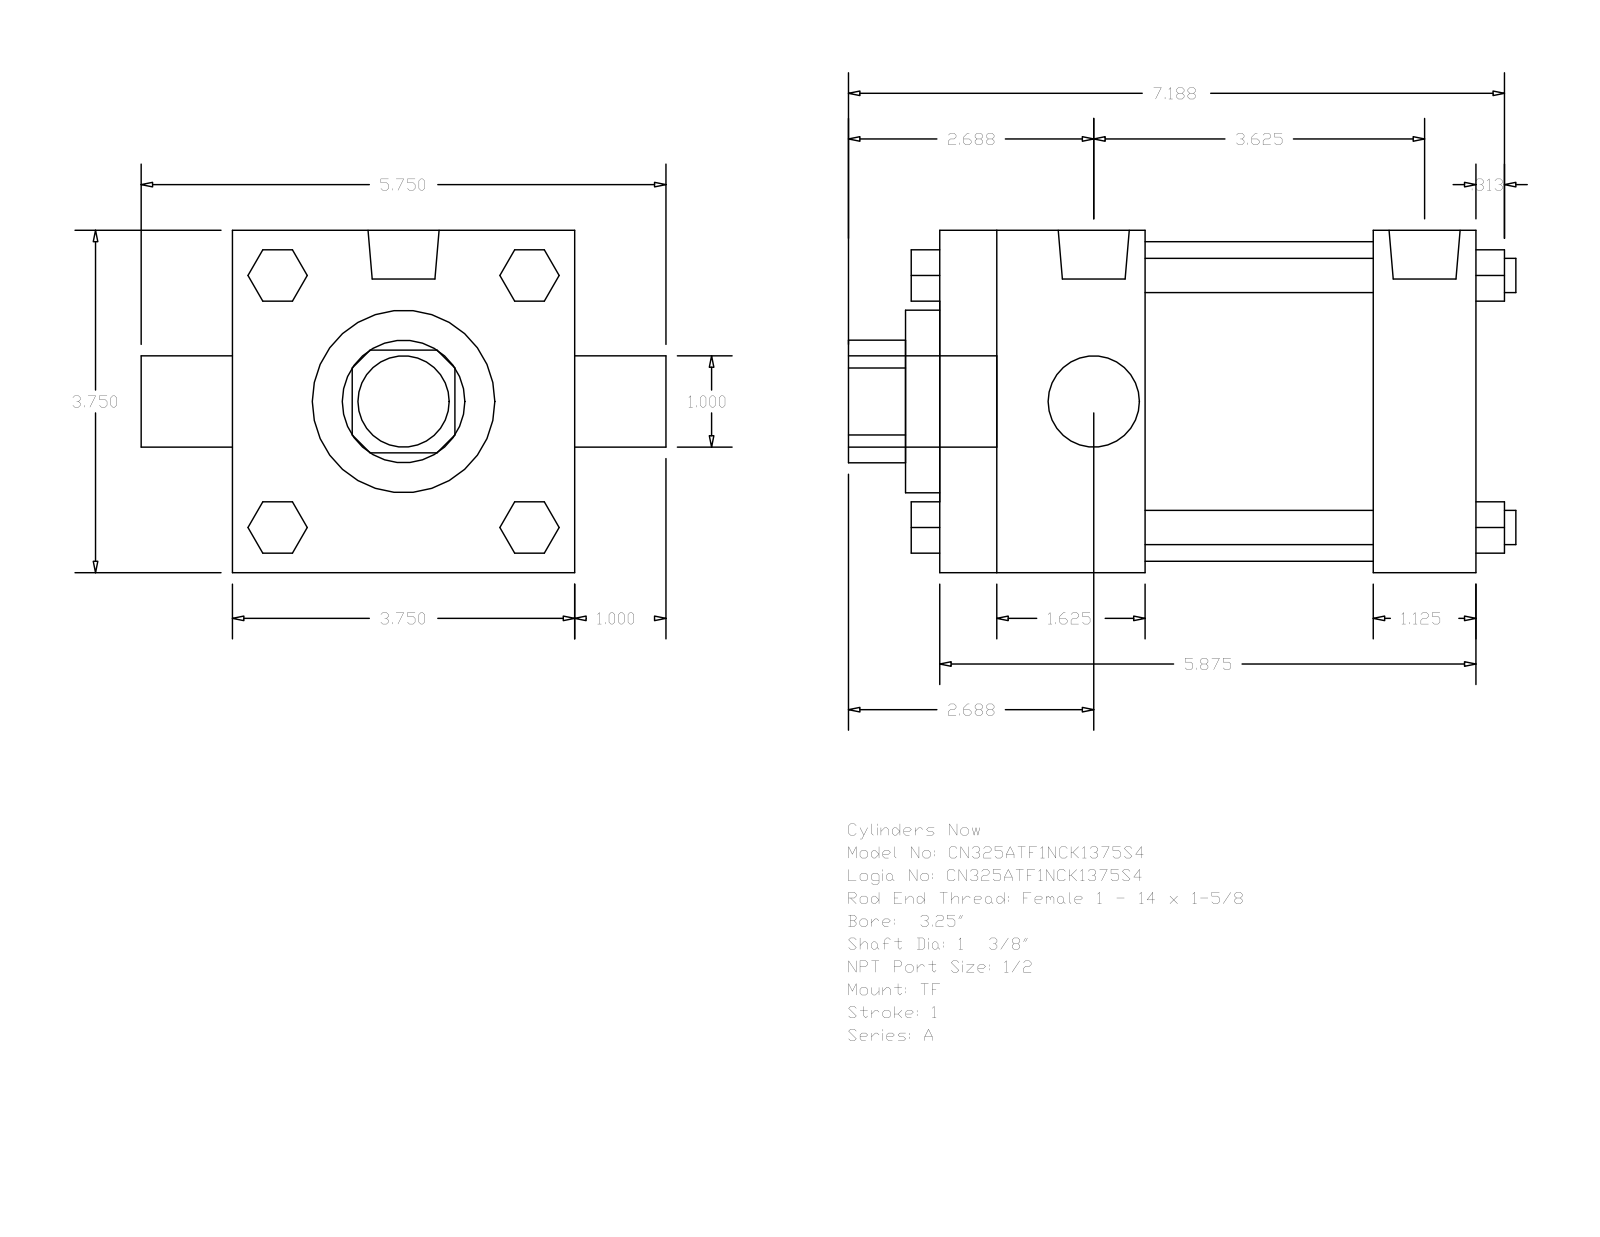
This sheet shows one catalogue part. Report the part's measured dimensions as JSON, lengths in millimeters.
{"part_name": "A_TF__0325_1.375", "step_written_by": "GSSL Pune (CONFIG_CONTROL_DESIGN)", "units": "millimeters", "bodies": {"solids": 0, "faces": 120, "planar": 92, "cylindrical": 28, "other": 0}, "overall_size": [185.74, 146.05, 95.25], "round_holes": [[25.4, 1], [34.92, 1], [50.8, 1], [88.9, 1]], "round_bosses_or_shafts": [[9.53, 4], [8.73, 3], [19.77, 2], [25.4, 1]], "partial_cylinders_radius": [[17.06, 1]], "face_to_face_distances": [95.24, 149.22, 120.65, 28.57, 57.15, 63.5, 92.07, 9.52, 66.67, 130.17]}
